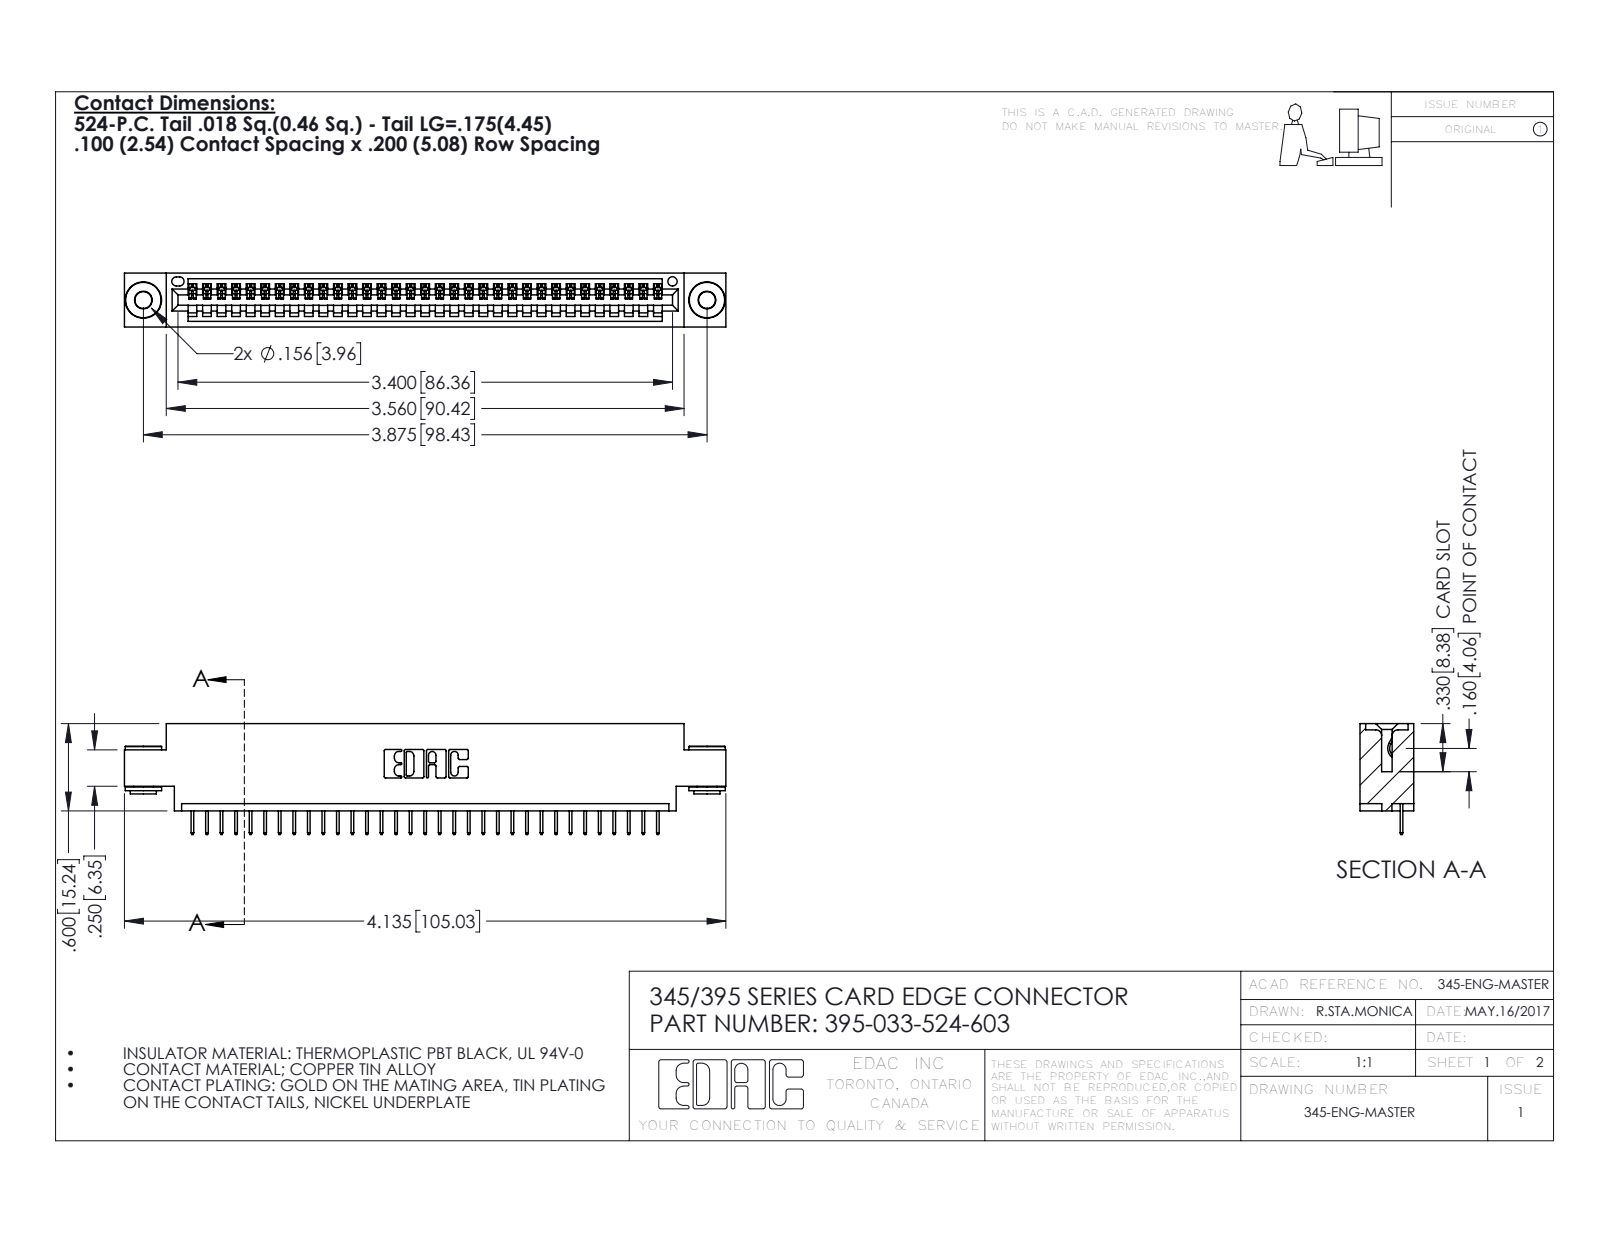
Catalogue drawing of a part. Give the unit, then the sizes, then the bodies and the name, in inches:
Units: inches
Overall size (bounding box): 4.135 × 0.762 × 0.37
Round holes (diameter × count): ⌀0.116 ×2, ⌀0.156 ×2, ⌀0.064 ×1
Round bosses / shafts (diameter × count): ⌀0.25 ×2, ⌀0.18 ×2, ⌀0.136 ×2
Partial cylindrical surfaces — rounded edges, fillets, slot ends (radius × count): R0.006 ×66, R0.01 ×22, R0.007 ×6, R0.031 ×6, R0.026 ×3, R0.031 ×2, R0.04 ×2, R0.014 ×1
Main face-to-face distances: 0.072, 0.298, 0.37, 0.2, 0.098, 0.272, 0.025, 0.225, 0.175, 0.072
Hole centre spacings: 0.27, 3.64, 3.875
Volume: 0.591 in³ · Surface area: 19.63 in²
Bodies: 36 solids, 2214 faces (1612 planar, 594 cylindrical, 8 other)
Part name (STEP PRODUCT): 345-250-002_345-250-002-102; 345-292-001_345-293-124; 345 Part_0.170 Offset - 0.156 Dia-TH; 395-033-524-603
STEP written by: SolidWorks 2016 (CONFIG_CONTROL_DESIGN)
